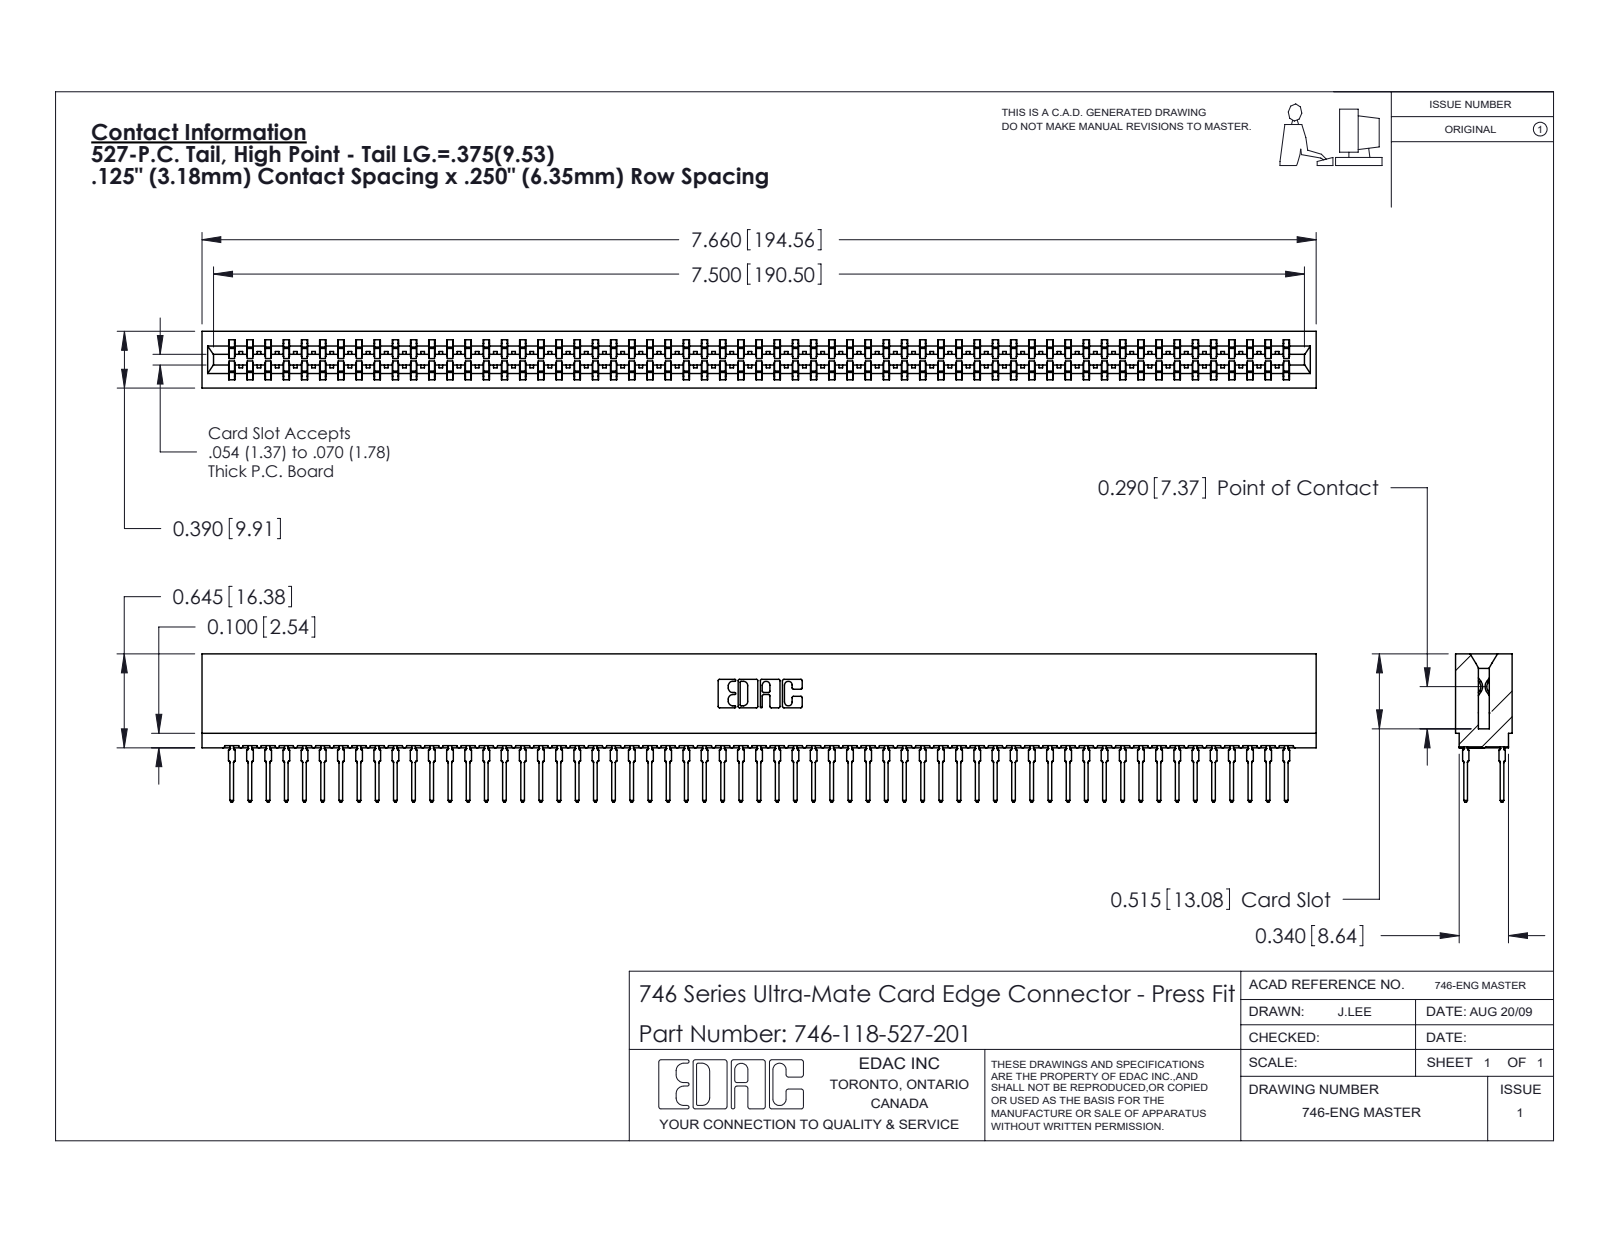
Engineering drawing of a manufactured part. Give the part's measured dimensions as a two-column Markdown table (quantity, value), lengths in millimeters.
| quantity | value |
| --- | --- |
| part name | 746 Part_.515 Slot Depth - 01; 746-292-001_527; 746-118-527-201 |
| STEP written by | SolidWorks 2020 (CONFIG_CONTROL_DESIGN) |
| units | millimeters |
| bodies | 119 solids, 10658 faces (5483 planar, 2107 cylindrical, 3068 other) |
| overall size | 194.6 × 25.9 × 9.9 |
| volume | 20 930 mm³ |
| surface area | 34 880 mm² |
| partial cylindrical surfaces (radius × count) | 0.5 × 236, 0.4 × 60, 0.3 × 22, 0.1 × 8, 0.3 × 8, 0.2 × 6, 0.8 × 6, 0.7 × 3 |
| main face-to-face distances | 1.4, 8.5, 9.9, 0.6, 6.4, 7.8, 7, 2.1, 4.4, 4 |
